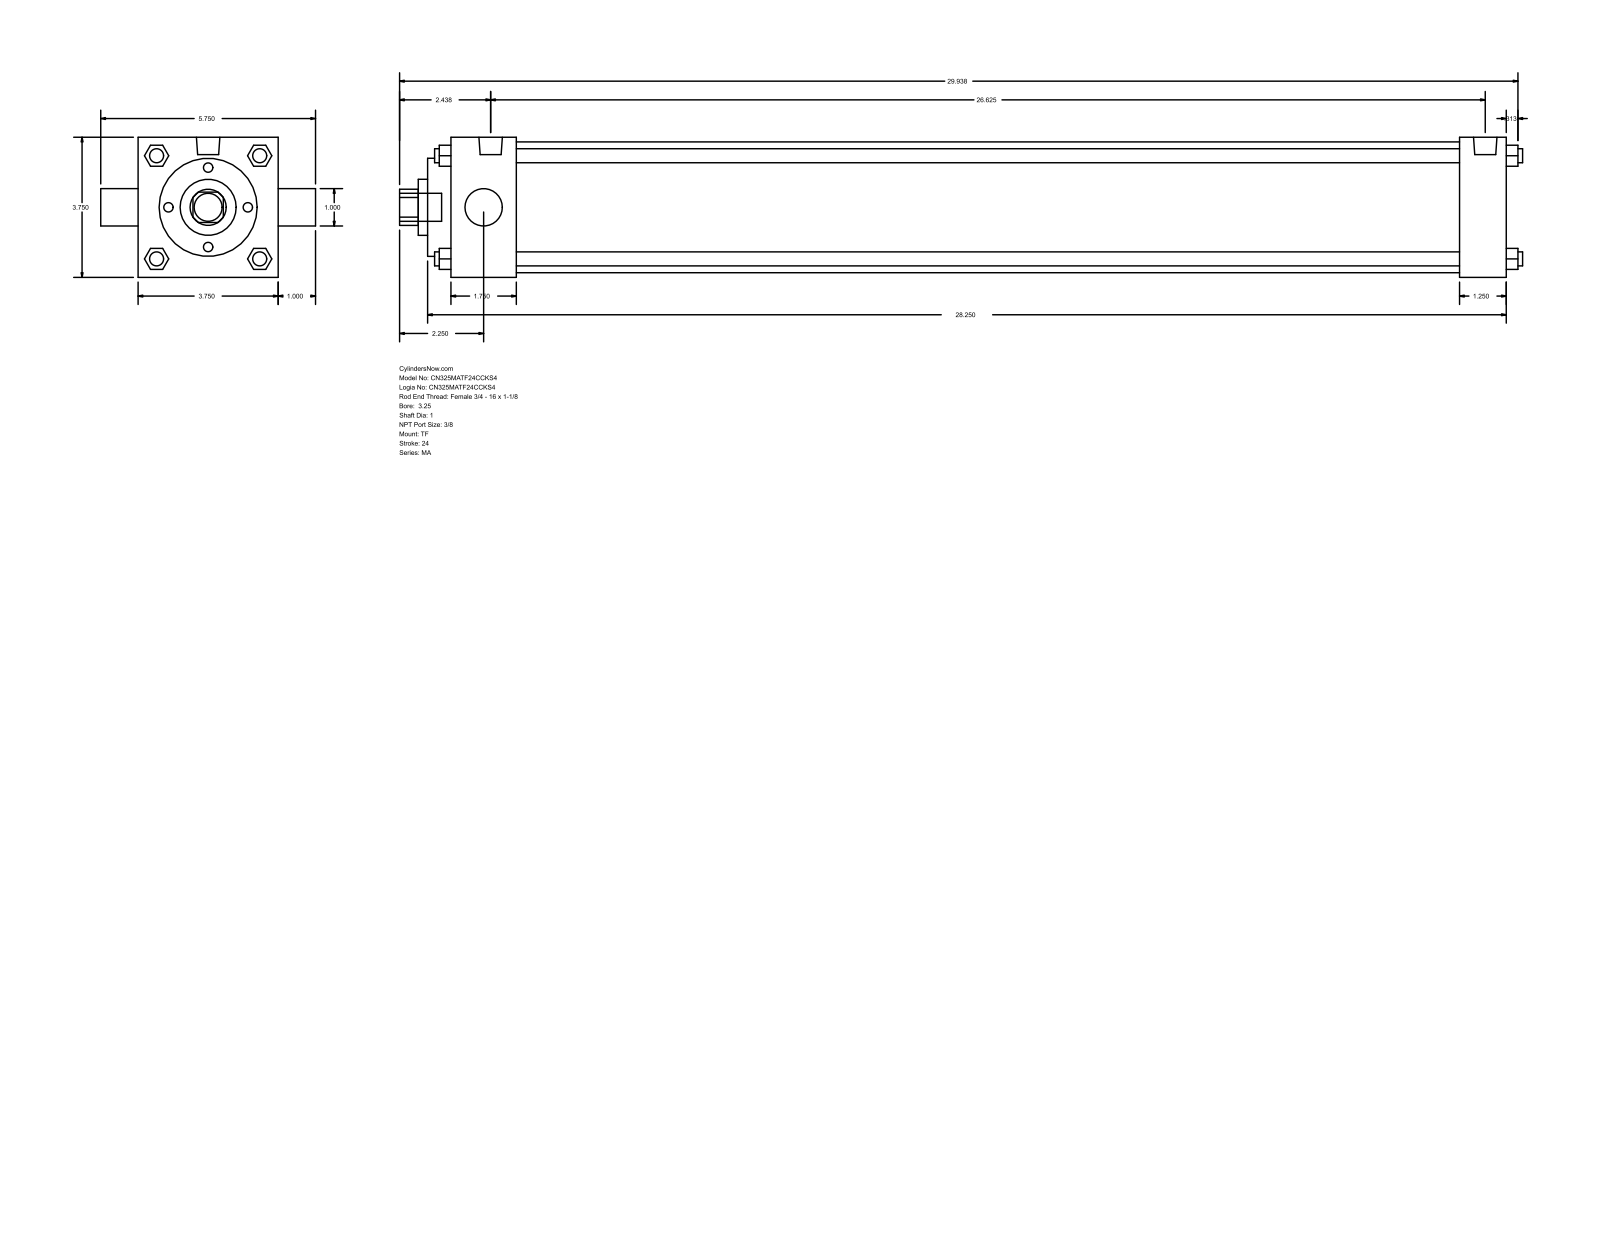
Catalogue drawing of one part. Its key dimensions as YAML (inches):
part_name: "MA_TF__0325_1"
step_written_by: "GSSL Pune (CONFIG_CONTROL_DESIGN)"
units: inches
bodies: {solids: 0, faces: 122, planar: 93, cylindrical: 29, other: 0}
overall_size: [30.063, 5.75, 3.75]
round_holes:
  - {diameter: 1, count: 2}
  - {diameter: 1.5, count: 1}
  - {diameter: 2.625, count: 1}
  - {diameter: 3.5, count: 1}
round_bosses_or_shafts:
  - {diameter: 0.375, count: 4}
  - {diameter: 0.437, count: 3}
  - {diameter: 0.627, count: 2}
  - {diameter: 0.75, count: 1}
partial_cylinders:
  - {radius: 0.484, count: 1}
face_to_face_distances: [3.75, 28.25, 0.625, 1.75, 27, 25.25, 26.5, 1.25, 2.375, 27.625]
